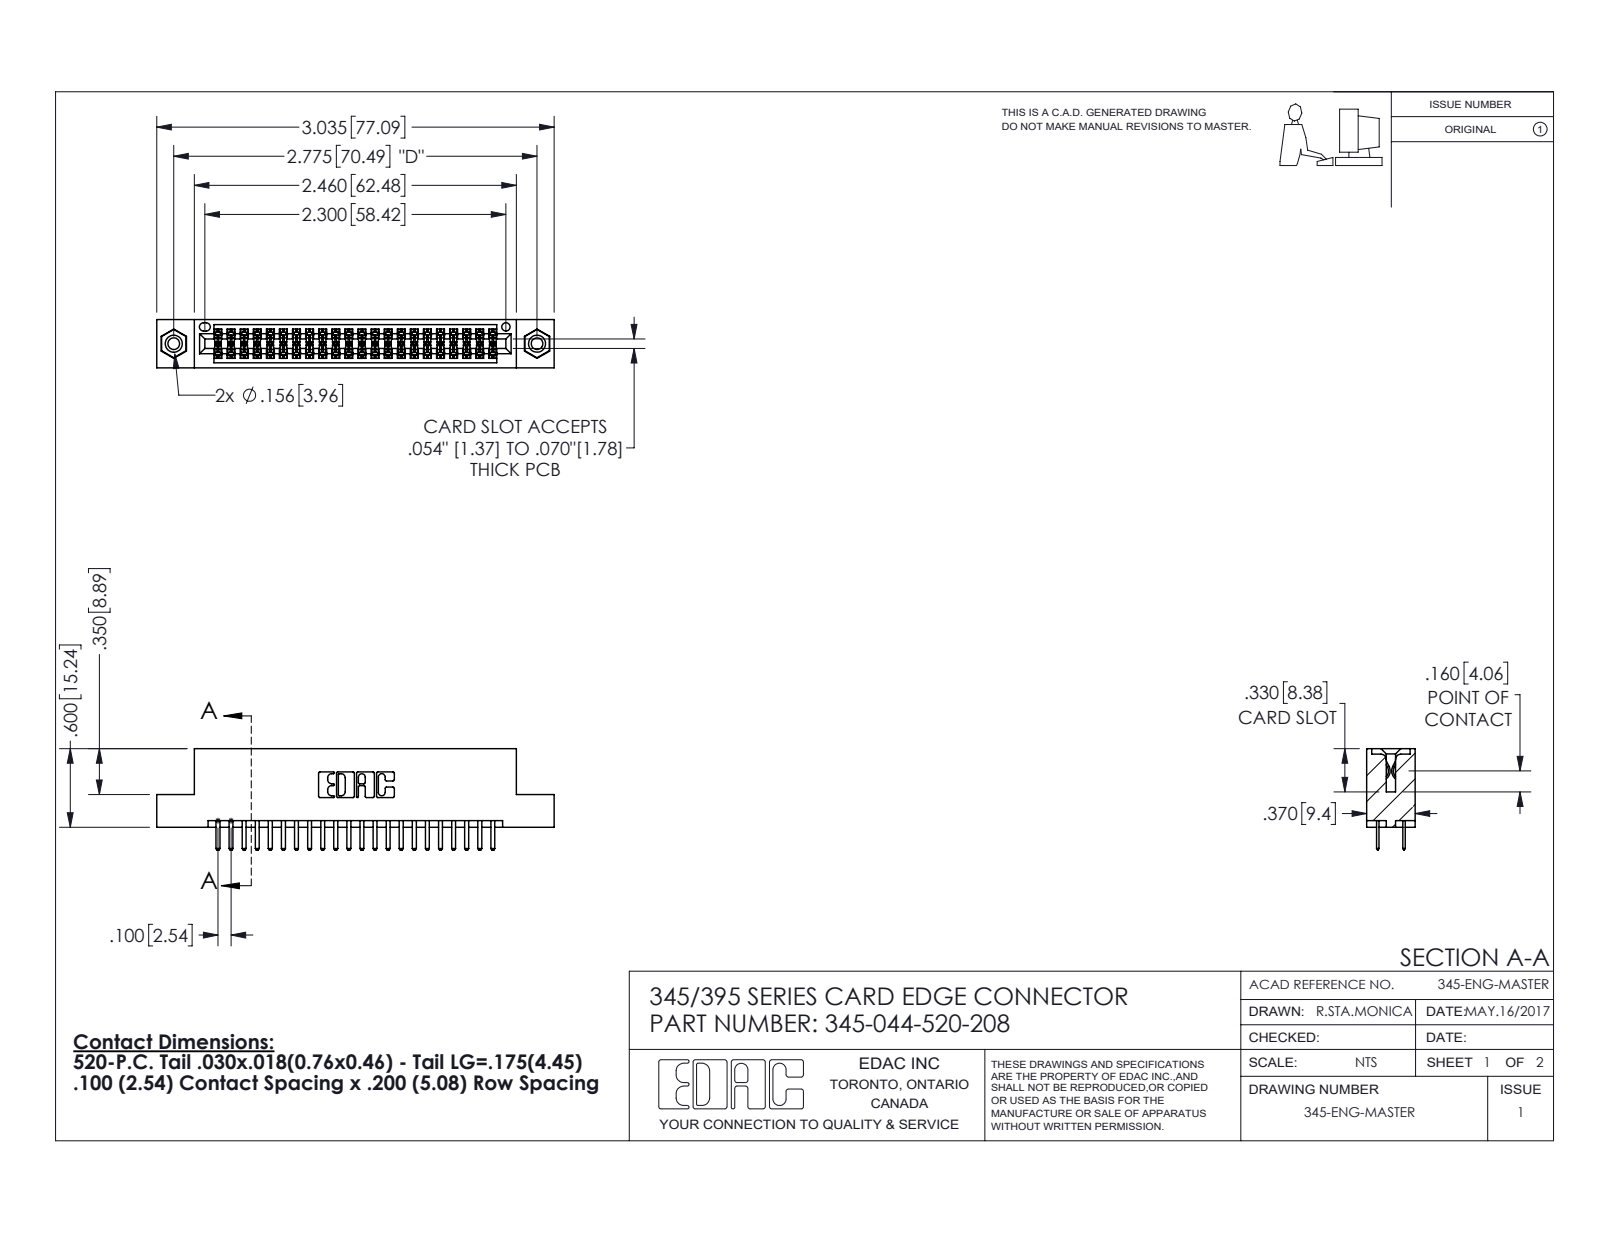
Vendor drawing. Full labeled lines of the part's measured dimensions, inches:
Part name (STEP PRODUCT): 345-250-001_345-250-003-102; 345-044-520-208; 345 Part_Flush Mounting Lugs - 0.156 Dia-TI; 345-292-001_345-293-120
STEP written by: SolidWorks 2016 (CONFIG_CONTROL_DESIGN)
Units: inches
Bodies: 47 solids, 2562 faces (1652 planar, 894 cylindrical, 16 other)
Overall size (bounding box): 3.035 × 0.775 × 0.37
Volume: 0.444 in³ · Surface area: 16.03 in²
Round holes (diameter × count): ⌀0.089 ×2, ⌀0.125 ×2, ⌀0.156 ×2, ⌀0.064 ×1
Round bosses / shafts (diameter × count): ⌀0.155 ×2
Partial cylindrical surfaces — rounded edges, fillets, slot ends (radius × count): R0.006 ×66, R0.01 ×48, R0.01 ×22, R0.007 ×6, R0.031 ×6, R0.026 ×3, R0.014 ×2, R0.019 ×2
Main face-to-face distances: 0.072, 0.298, 0.2, 0.37, 0.098, 0.272, 0.025, 0.225, 0.022, 0.072
Hole centre spacings: 0.27, 2.541, 2.775
